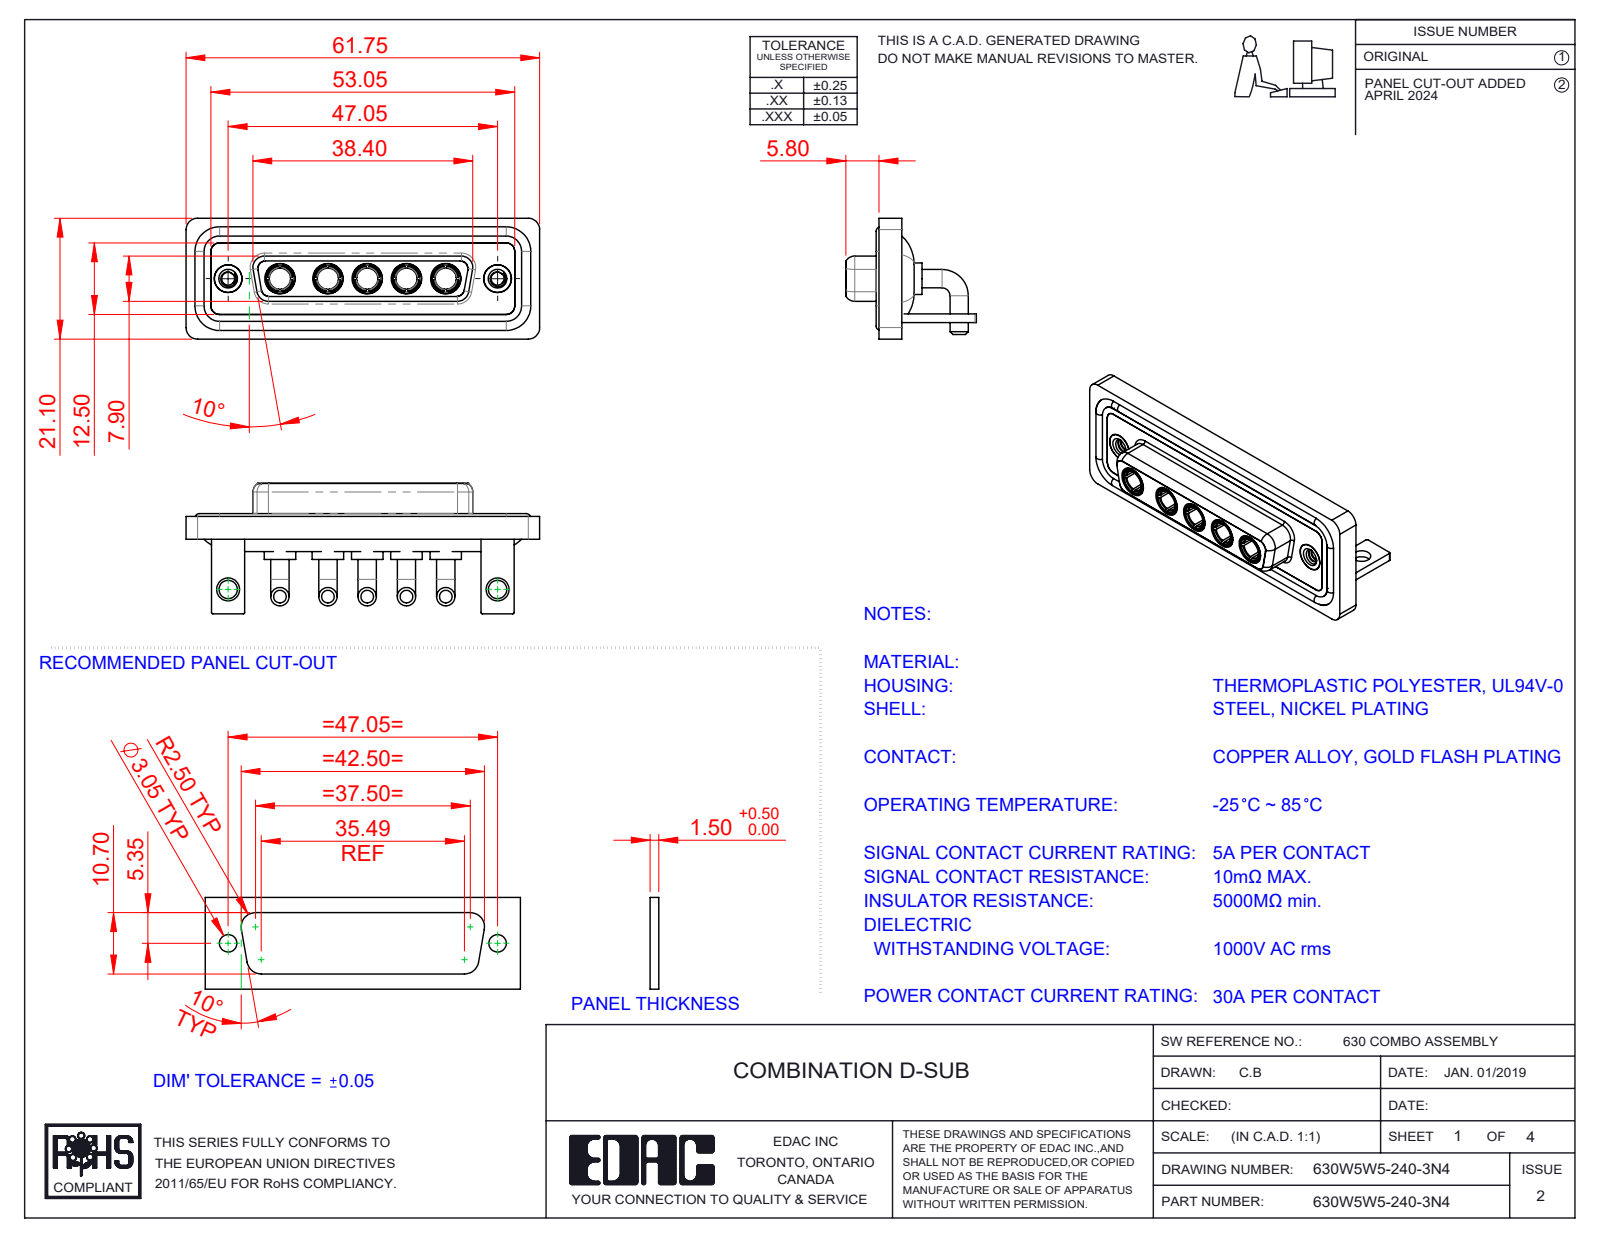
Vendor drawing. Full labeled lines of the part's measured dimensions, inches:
Part name (STEP PRODUCT): 630Combo Waterproof Housing_25 Contacts; 630Combo Shell Rear_25 Contacts; 630Combo Shell Front_25 Contacts; 630W5W5-140-3N4 (+4 more)
STEP written by: SolidWorks 2023 (CONFIG_CONTROL_DESIGN)
Units: inches
Bodies: 19 solids, 824 faces (270 planar, 337 cylindrical, 217 other)
Overall size (bounding box): 2.431 × 0.898 × 0.831
Volume: 0.546 in³ · Surface area: 22.69 in²
Round holes (diameter × count): ⌀0.191 ×7, ⌀0.146 ×5, ⌀0.209 ×5, ⌀0.089 ×2, ⌀0.126 ×2, ⌀0.157 ×2, ⌀0.159 ×2, ⌀0.197 ×2
Round bosses / shafts (diameter × count): ⌀0.126 ×10, ⌀0.217 ×5, ⌀0.205 ×5, ⌀0.195 ×5, ⌀0.187 ×5, ⌀0.148 ×5, ⌀0.063 ×4, ⌀0.195 ×2
Partial cylindrical surfaces — rounded edges, fillets, slot ends (radius × count): R0.079 ×19, R0.059 ×18, R0.01 ×16, R0.053 ×8, R0.063 ×8, R0.02 ×5, R0.083 ×5, R0.024 ×4
Main face-to-face distances: 0.016, 0.071, 0.114, 0.146, 0.059, 0.161, 0.043, 0.055, 0.063, 0.098
Hole centre spacings: 0.27, 0.356, 1.496, 1.852, 0.27, 0.33, 0.54, 0.541
